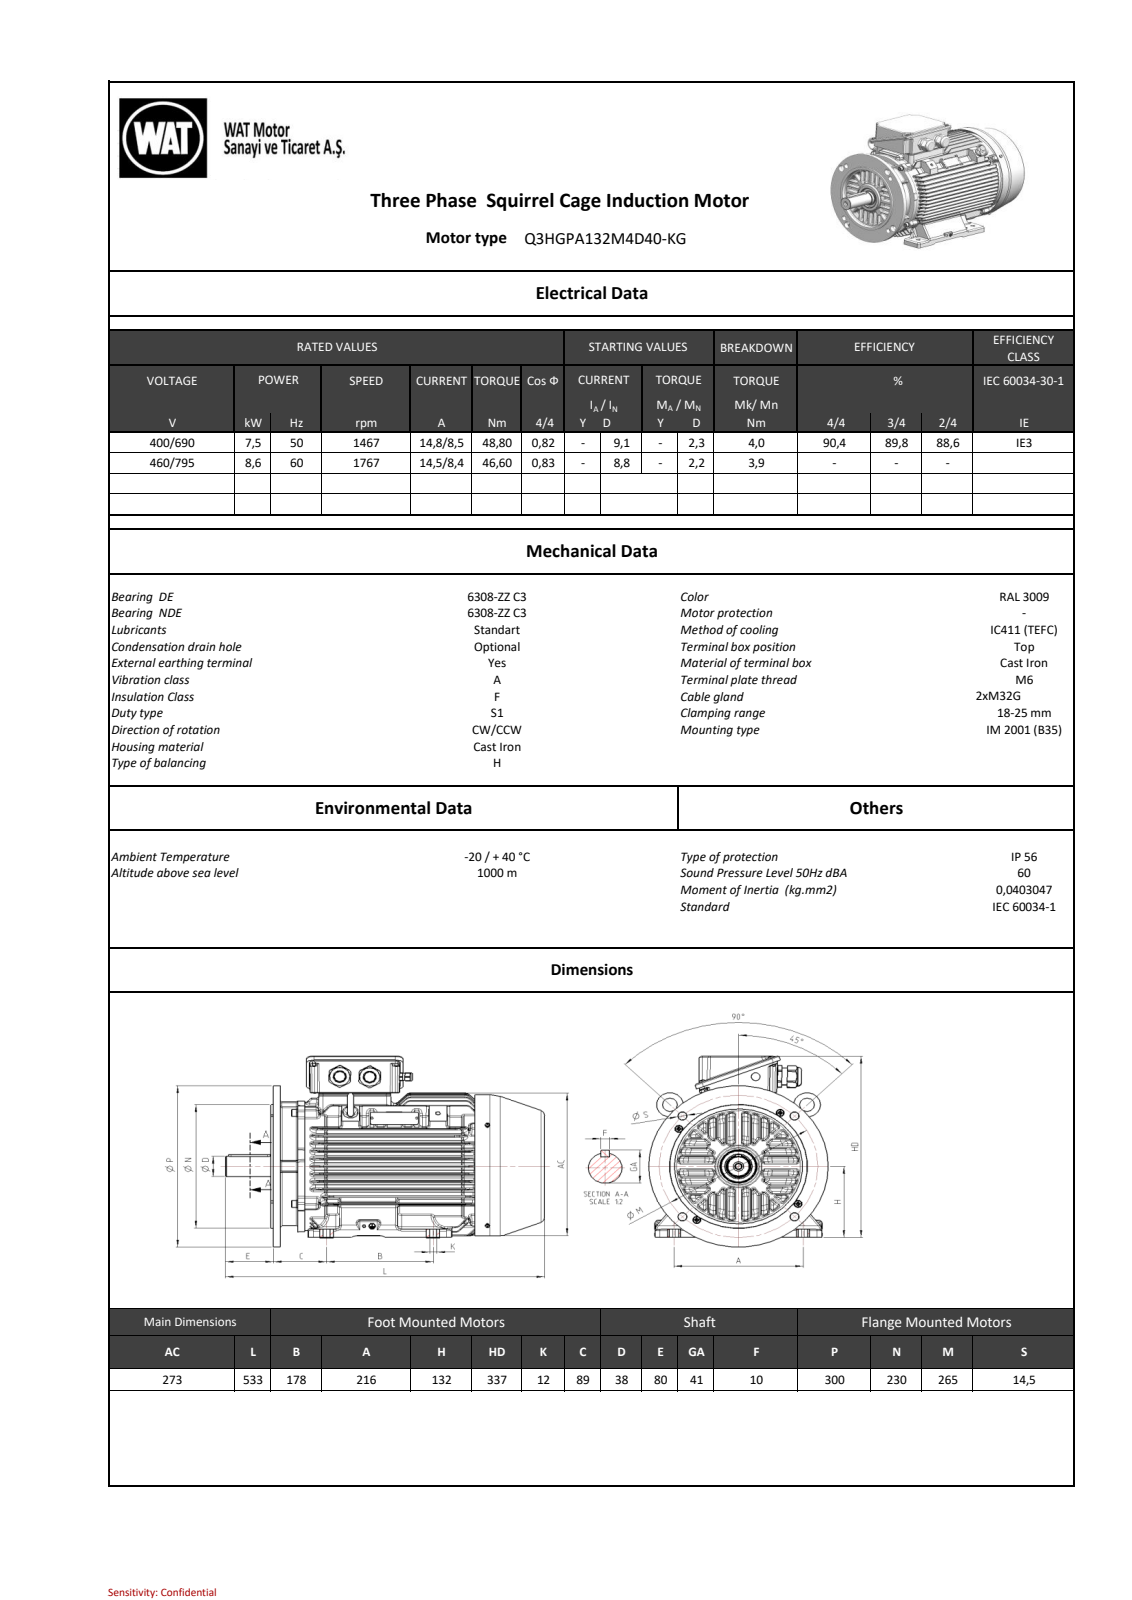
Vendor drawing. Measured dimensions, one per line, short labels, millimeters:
name: 260021E4F5C7p83d
written by: SIEMENS PLM Software NX 11.0 (AUTOMOTIVE_DESIGN)
unit: mm
bodies: 0 solids, 6332 faces (1125 planar, 1750 cylindrical, 3457 other)
size: 533 × 355.41 × 300
holes: 8× ⌀5.5, 8× ⌀6.8, 4× ⌀8.5, 4× ⌀14, 2× ⌀2.5, 2× ⌀4.2, 2× ⌀19, 2× ⌀21, 1× ⌀5, 1× ⌀10.3, 1× ⌀13, 1× ⌀34.2
bosses: 4× ⌀13, 4× ⌀8.65, 4× ⌀8, 2× ⌀36, 2× ⌀34.5, 2× ⌀31.25, 1× ⌀300, 1× ⌀267
rounds: 299× R4, 175× R3, 106× R1.5, 84× R2, 64× R1.8, 32× R6, 24× R28, 24× R35
face distances: 13.76, 55.94, 13.83, 27.59, 110.18, 12, 82.59, 96.35, 13.9, 27.73
hole spacings: 136, 121.5, 171.83, 123.22, 183.52, 42.2, 123.21, 139.38
